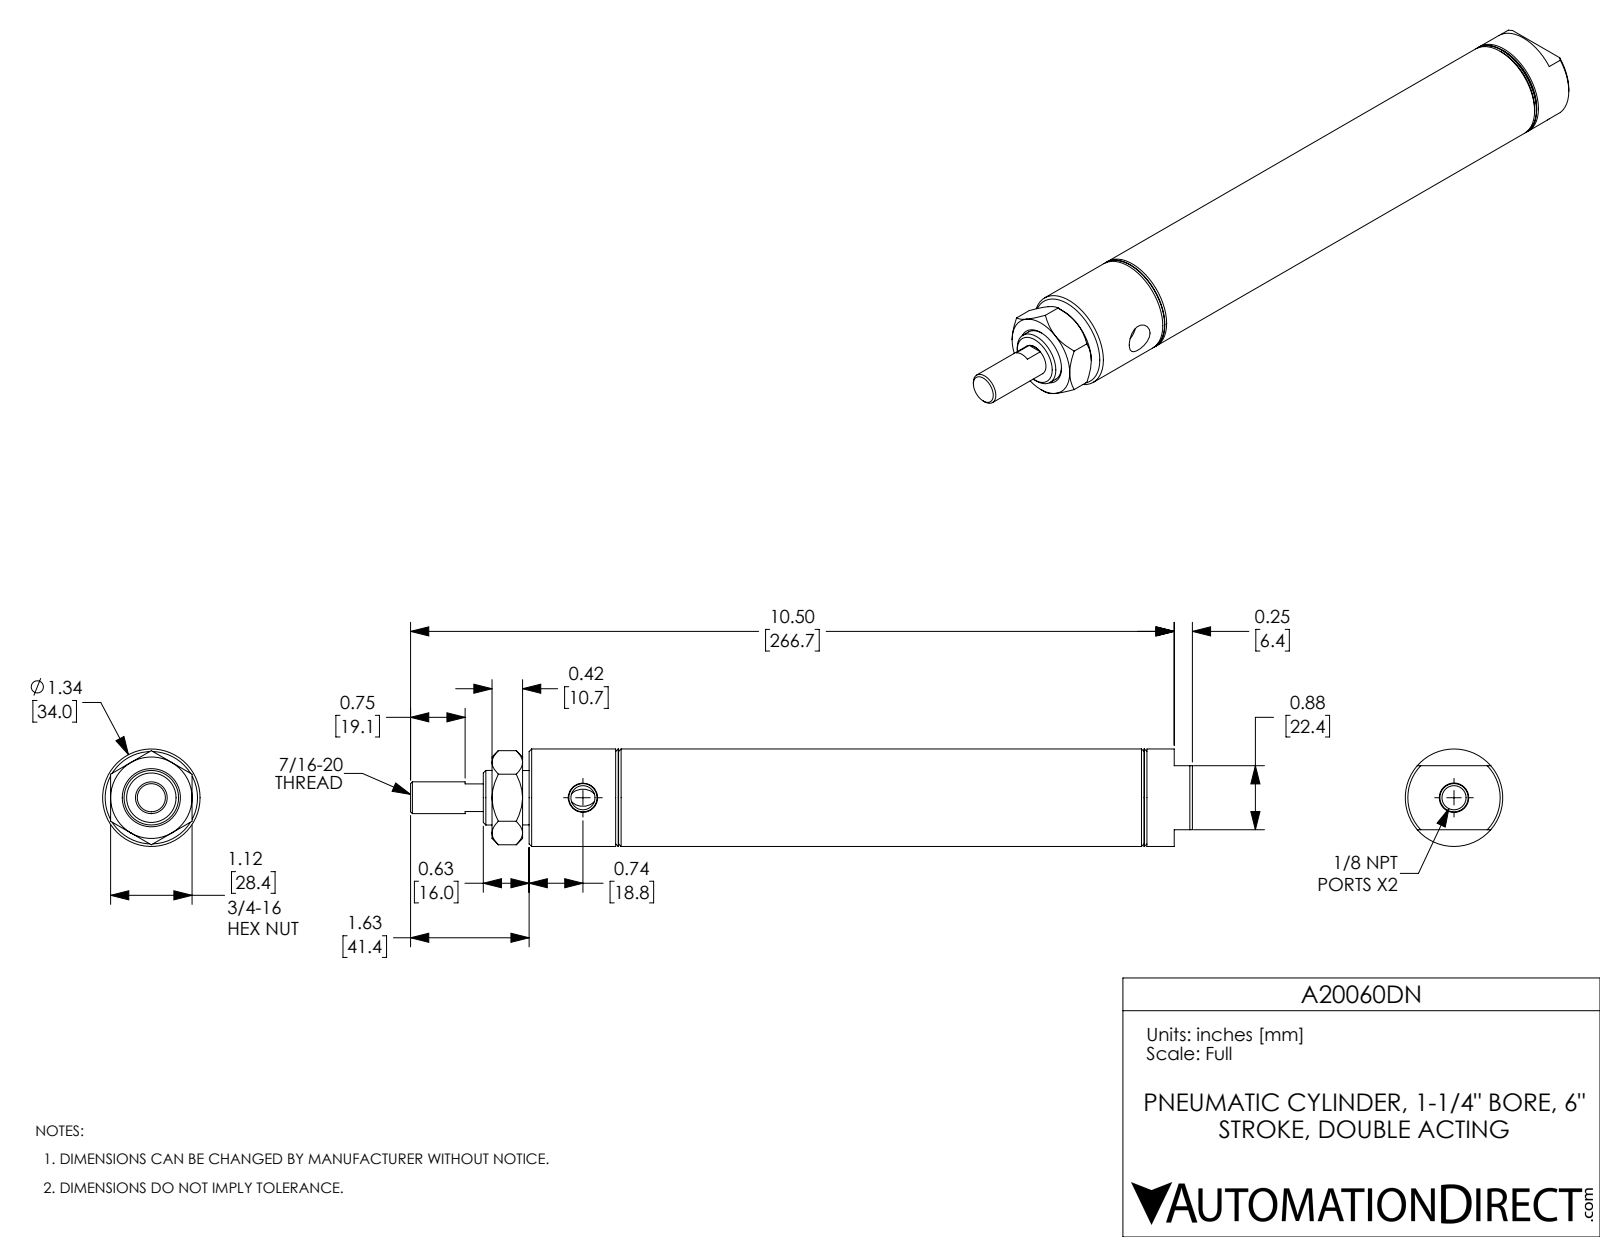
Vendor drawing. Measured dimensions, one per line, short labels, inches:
name: A20060DN_Mounting Nut_D-3556; A20060DN-Rod; A20060DN-MainBody; A20060DN
written by: SolidWorks 2017 (AUTOMOTIVE_DESIGN)
unit: in
bodies: 3 solids, 100 faces (33 planar, 28 cylindrical, 39 other)
size: 10.75 × 1.34 × 1.34
volume: 6.819 in³; area: 95.59 in²
holes: 2× ⌀0.332, 1× ⌀0.437, 1× ⌀0.75, 1× ⌀1.25
bosses: 1× ⌀1.34, 1× ⌀0.747
face distances: 6.5, 0.5, 6, 1.31, 1.81, 7.81, 9.12, 7.81, 7.31, 1.31
